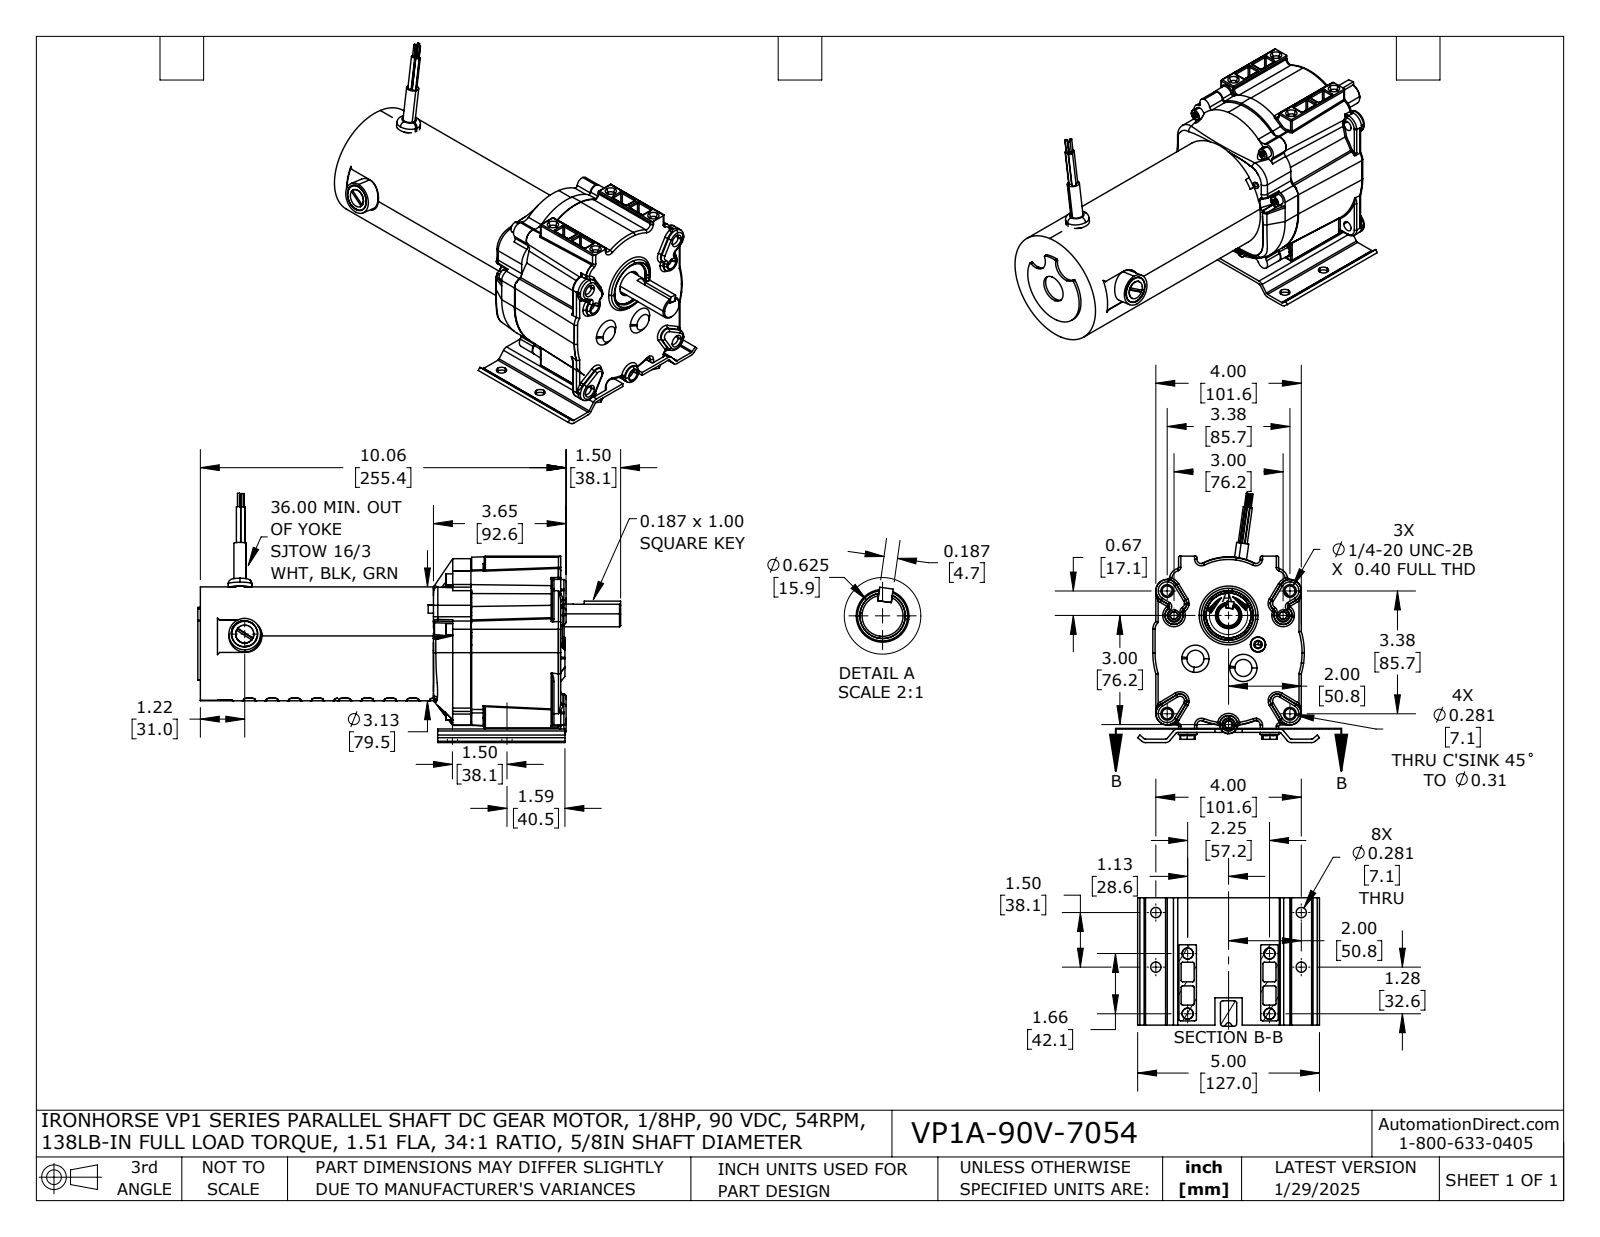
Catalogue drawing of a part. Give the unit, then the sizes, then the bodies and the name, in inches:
Units: inches
Overall size (bounding box): 11.627 × 6.854 × 5
Round holes (diameter × count): ⌀0.281 ×12, ⌀0.218 ×5, ⌀0.159 ×3, ⌀0.207 ×3, ⌀0.135 ×2, ⌀0.166 ×2, ⌀0.204 ×2, ⌀0.397 ×2, ⌀0.688 ×2, ⌀0.875 ×2, ⌀0.75 ×1, ⌀0.813 ×1
Round bosses / shafts (diameter × count): ⌀0.307 ×5, ⌀0.19 ×5, ⌀0.51 ×4, ⌀0.3 ×4, ⌀0.12 ×3, ⌀0.06 ×3, ⌀0.873 ×2, ⌀0.733 ×2
Partial cylindrical surfaces — rounded edges, fillets, slot ends (radius × count): R0.03 ×52, R0.031 ×38, R0.062 ×23, R0.12 ×18, R0.156 ×18, R0.19 ×10, R0.151 ×9, R0.161 ×9
Main face-to-face distances: 0.095, 2.449, 3.5, 1.051, 9.44, 6.991, 5.94, 0.47, 6.97, 9.91
Hole centre spacings: 1.5, 3.375, 1.691, 0.492, 0.698, 1.224, 1.426, 1.552
Volume: 98.93 in³ · Surface area: 345.4 in²
Bodies: 10 solids, 2472 faces (654 planar, 701 cylindrical, 1117 other)
Part name (STEP PRODUCT): VP1A-90V-7054
STEP written by: SolidWorks 2024 (AUTOMOTIVE_DESIGN)
